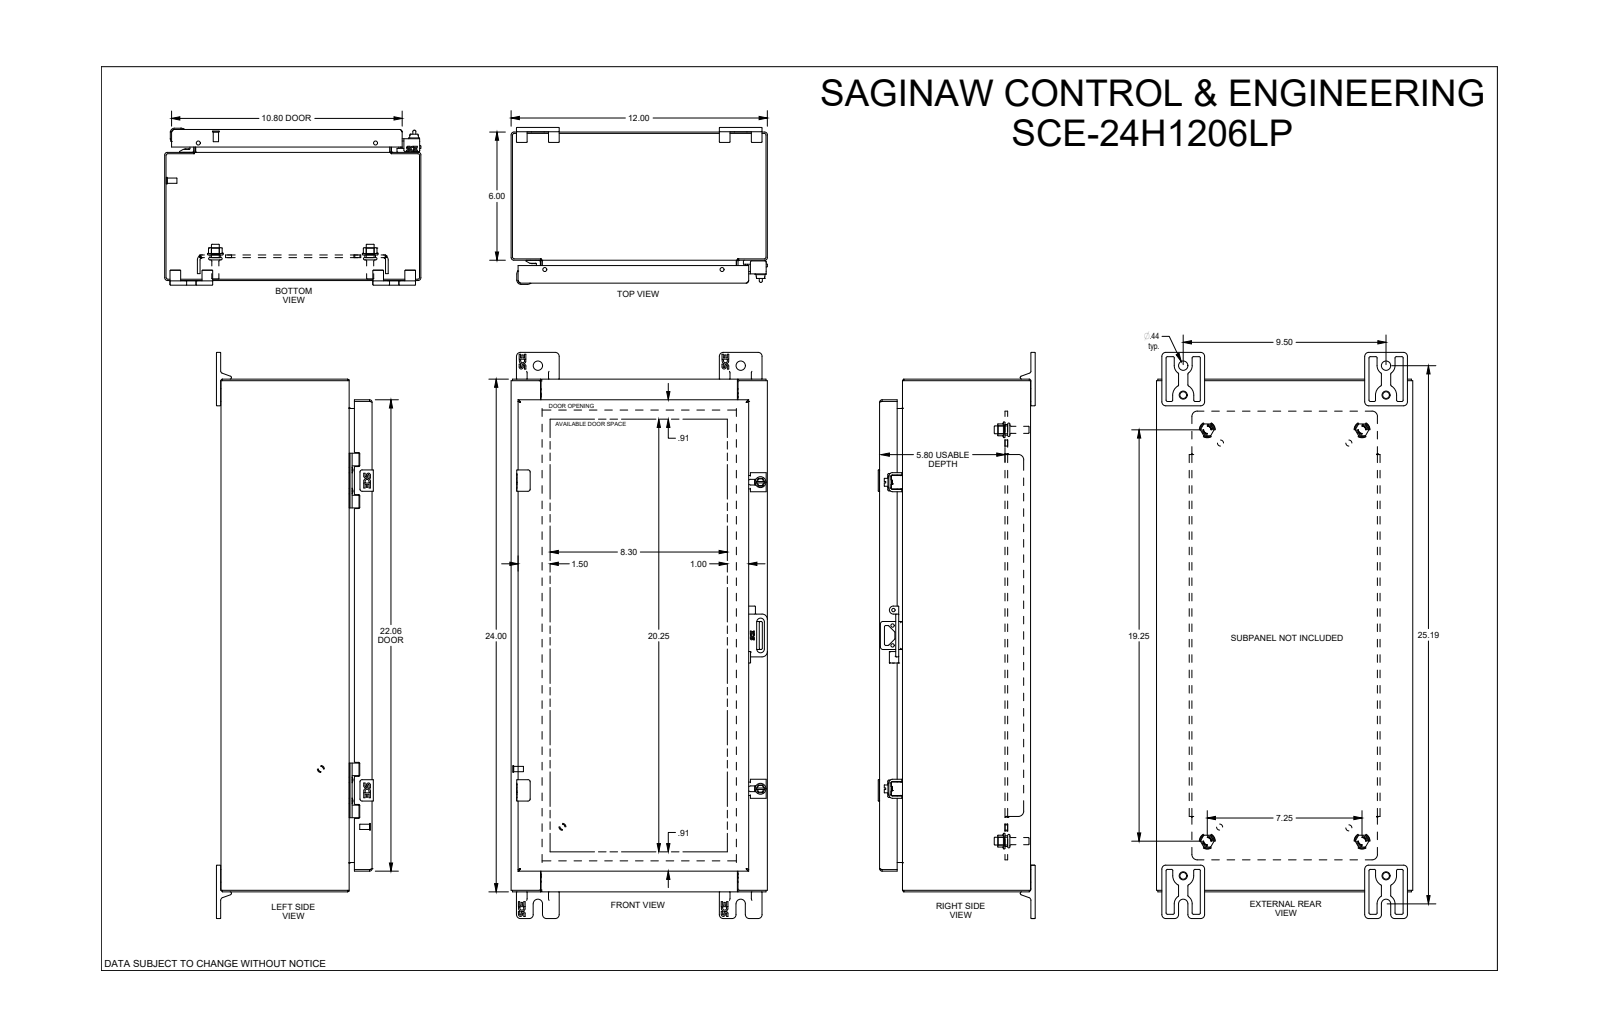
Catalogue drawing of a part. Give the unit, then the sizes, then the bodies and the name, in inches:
Units: inches
Overall size (bounding box): 26.5 × 12 × 7.348
Round holes (diameter × count): ⌀0.172 ×4, ⌀0.205 ×4, ⌀0.218 ×4, ⌀0.244 ×4, ⌀0.266 ×4, ⌀0.281 ×4, ⌀0.31 ×4, ⌀0.312 ×4, ⌀0.367 ×4, ⌀0.375 ×4, ⌀0.437 ×4, ⌀0.5 ×4
Round bosses / shafts (diameter × count): ⌀0.17 ×7, ⌀0.25 ×6, ⌀0.248 ×5, ⌀0.59 ×4, ⌀0.376 ×4, ⌀0.366 ×4, ⌀0.332 ×4, ⌀0.24 ×4
Partial cylindrical surfaces — rounded edges, fillets, slot ends (radius × count): R0.025 ×125, R0.01 ×114, R0.015 ×56, R0.03 ×37, R0.062 ×35, R0.06 ×30, R0.063 ×28, R0.185 ×21
Main face-to-face distances: 0.075, 11.925, 6.998, 6.923, 0.075, 7.073, 6.998, 5.923, 0.125, 1.2
Hole centre spacings: 14.5, 0.02, 0.493, 0.875, 0.985, 1.977, 8.531, 20.905
Bodies: 0 solids, 3917 faces (1504 planar, 1128 cylindrical, 1285 other)
Part name (STEP PRODUCT): SCE-24H1206LP
STEP written by: SolidWorks 2019 (CONFIG_CONTROL_DESIGN)
